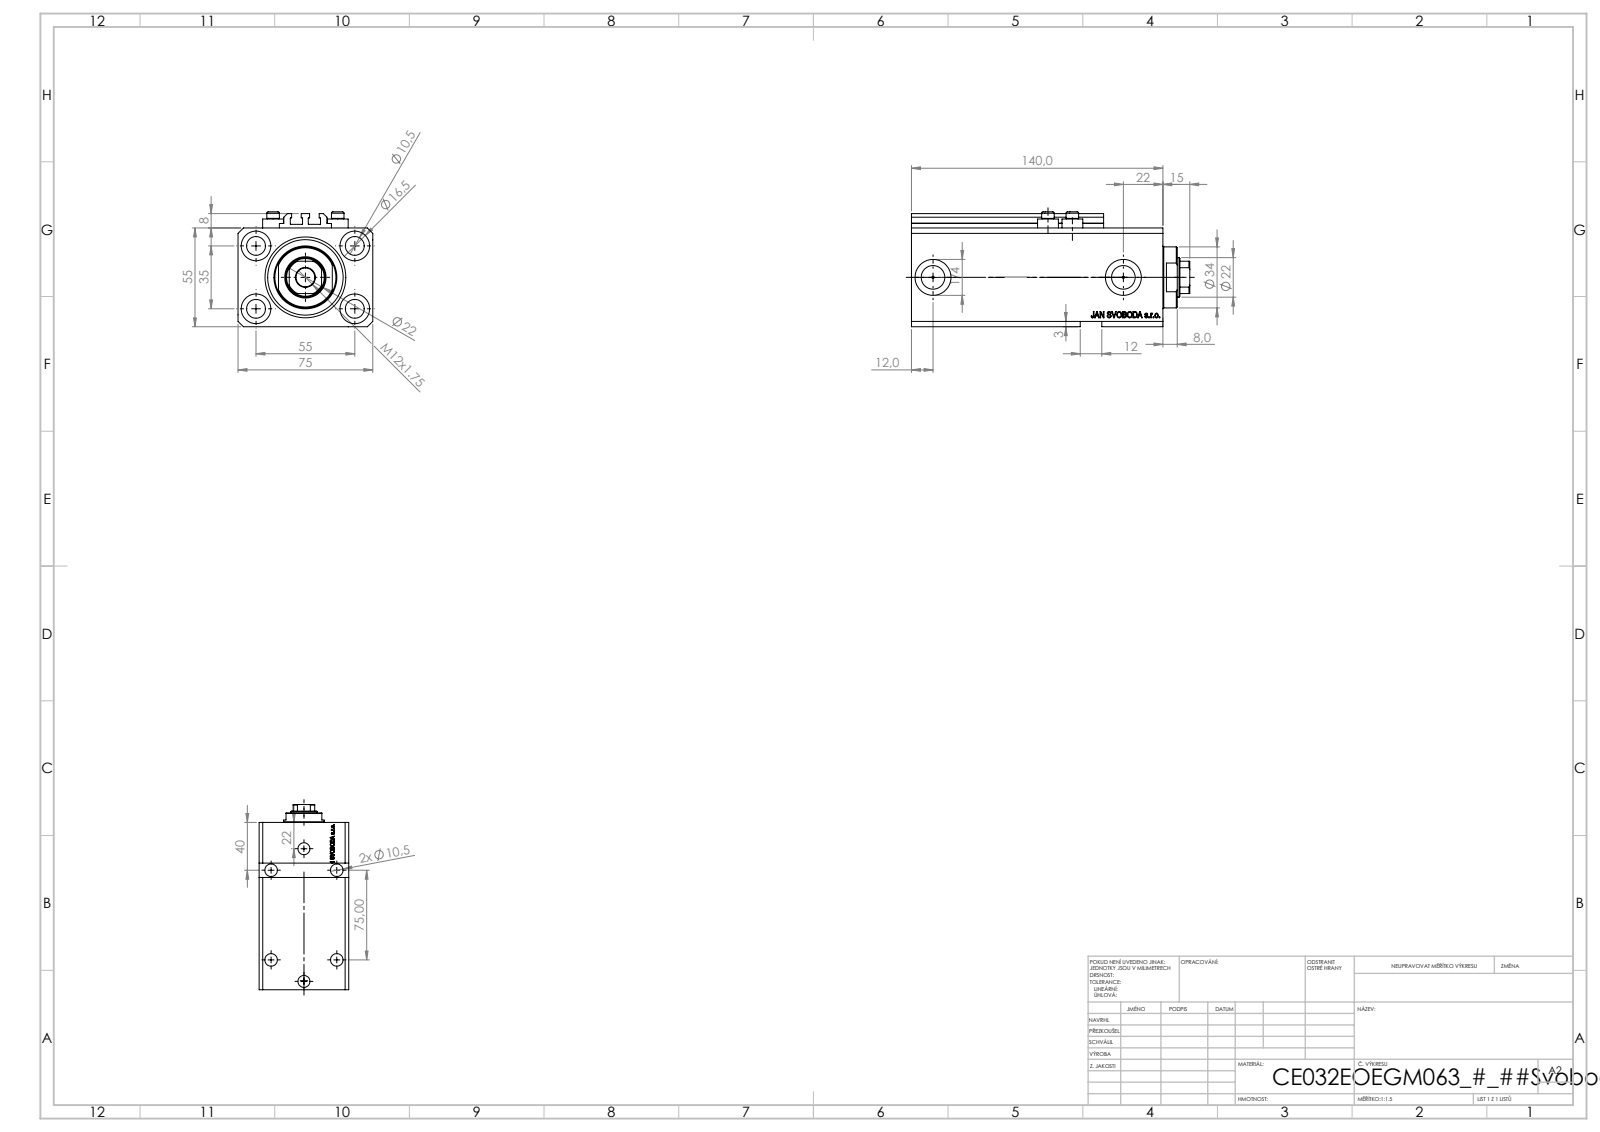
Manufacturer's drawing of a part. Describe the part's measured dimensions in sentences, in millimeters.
The part is named "V250CE_C_VCP; V250CE_E_Body; V250CE_VC_E; ALLEN BOLT V250CE". Its 3-D file was written by "SolidWorks 2019 (CONFIG_CONTROL_DESIGN)". It is 8 solids with 1084 faces: 514 planar, 146 cylindrical and 424 other. Overall it measures 155 by 75 by 64 millimeters. Its volume is 485 219 cubic millimeters and its surface area 115 303 square millimeters. Round holes: 9 of diameter 10.5, 4 of diameter 1.25, 4 of diameter 4, 4 of diameter 16.5, 2 of diameter 10, 2 of diameter 13.16, 2 of diameter 20, 1 of diameter 22, 1 of diameter 32, 1 of diameter 45. Round bosses or shafts: 4 of diameter 11.6, 4 of diameter 7, 1 of diameter 34. Partial cylindrical surfaces (rounded edges, fillets, slot ends): 10 of radius 0.2, 1 of radius 10.5. The main face-to-face distances are 55, 75, 15, 140, 125, 3, 9.9, 57, 115.1, 130.1. The hole center spacings are 32.6, 32.87, 55, 96.98, 13.6, 14.09, 25.81, 32.58.
